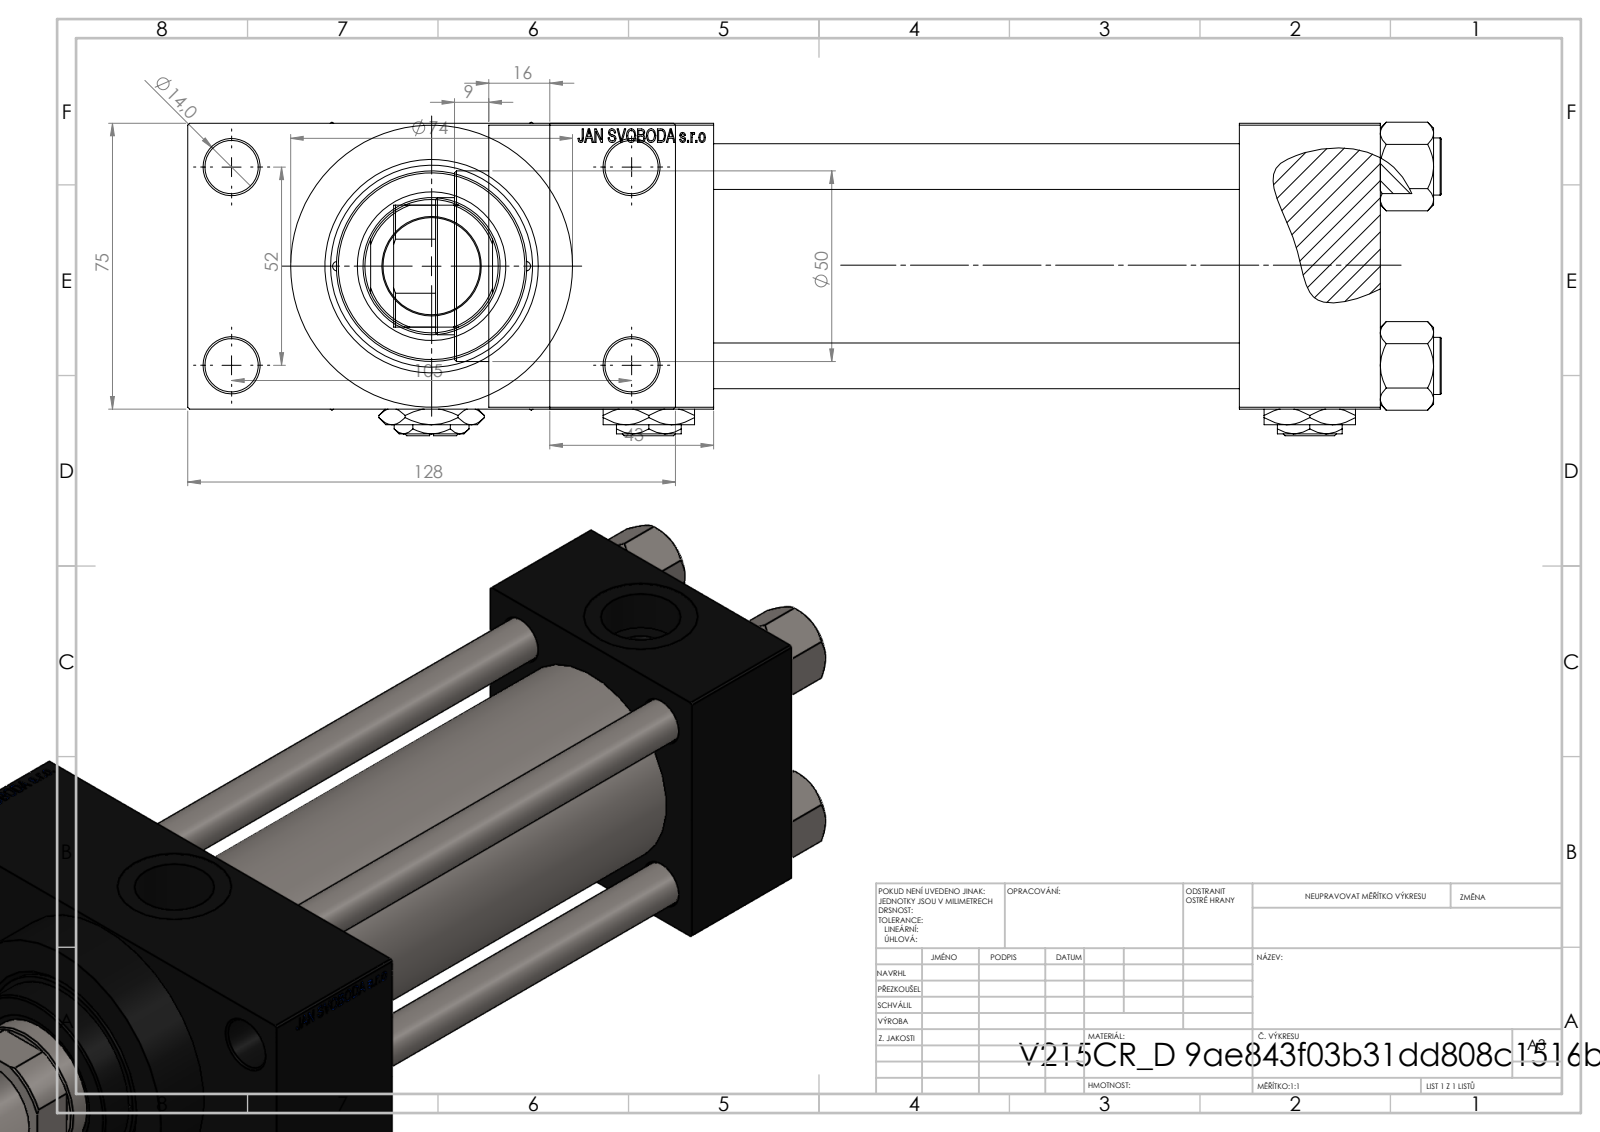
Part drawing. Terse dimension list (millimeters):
name: NUT_M5_D; V215CR_VCP_D; V215_VC_A; V215CR_D_Body (+2 more)
written by: SolidWorks 2019 (CONFIG_CONTROL_DESIGN)
unit: mm
bodies: 13 solids, 1215 faces (549 planar, 104 cylindrical, 562 other)
size: 275 × 128 × 82.27
volume: 979 314 mm³; area: 225 727 mm²
holes: 4× ⌀12, 4× ⌀14, 2× ⌀2.5, 2× ⌀7, 2× ⌀20.96, 2× ⌀30, 1× ⌀25.5, 1× ⌀36, 1× ⌀39, 1× ⌀41, 1× ⌀53
bosses: 4× ⌀15, 1× ⌀74, 1× ⌀56, 1× ⌀50
rounds: 1× R17.5
face distances: 75, 138, 37, 175, 26.5, 101.5, 218, 43, 181, 128
hole spacings: 26.19, 26.35, 36.98, 38.03, 52.3, 57.22, 58.43, 58.59
